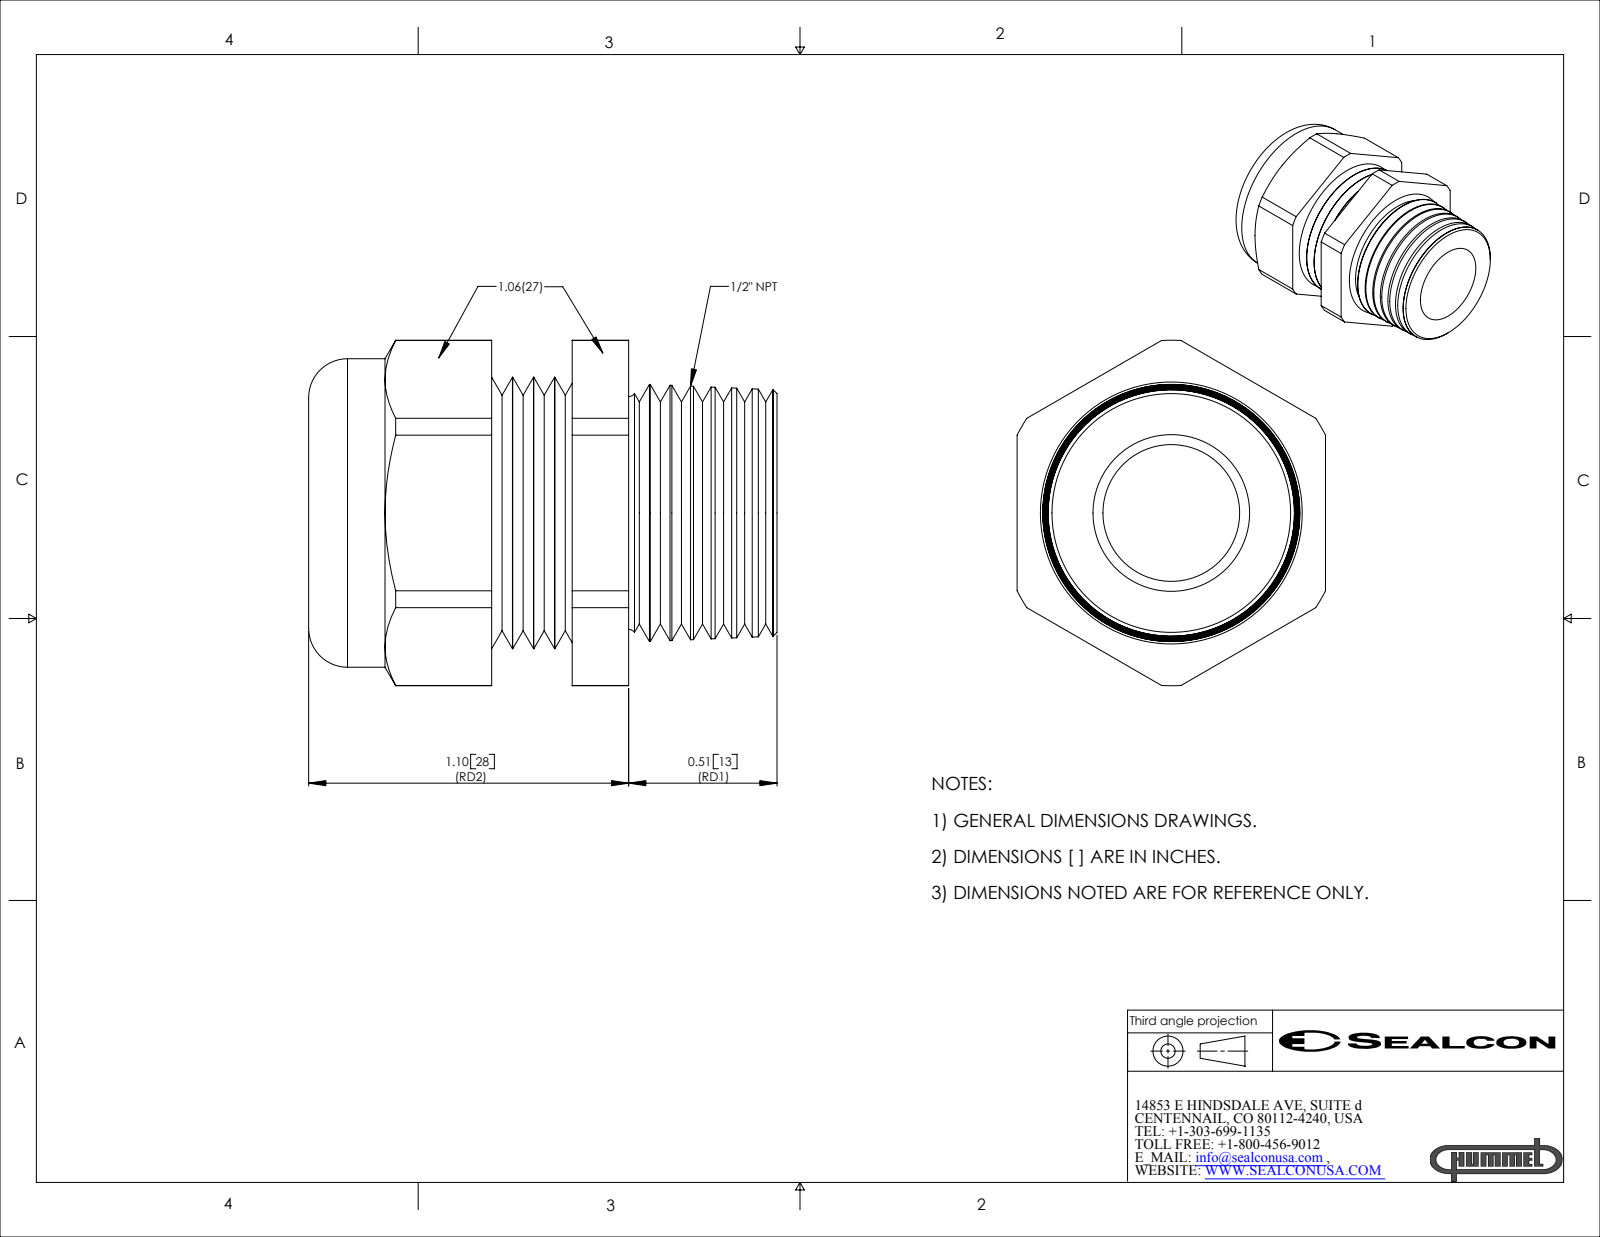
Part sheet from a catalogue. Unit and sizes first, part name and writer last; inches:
Units: inches
Overall size (bounding box): 1.61 × 1.187 × 1.06
Round holes (diameter × count): ⌀0.47 ×1, ⌀0.757 ×1
Round bosses / shafts (diameter × count): ⌀1.06 ×1, ⌀0.933 ×1
Partial cylindrical surfaces — rounded edges, fillets, slot ends (radius × count): R0.594 ×1
Main face-to-face distances: 1.06, 0.837, 1.347, 0.51, 0.643, 0.194, 0.704, 0.367, 0.277, 0.471
Volume: 0.883 in³ · Surface area: 13.05 in²
Bodies: 2 solids, 126 faces (20 planar, 30 cylindrical, 76 other)
Part name (STEP PRODUCT): CD16NR-BK
STEP written by: SolidWorks 2007 (CONFIG_CONTROL_DESIGN)
